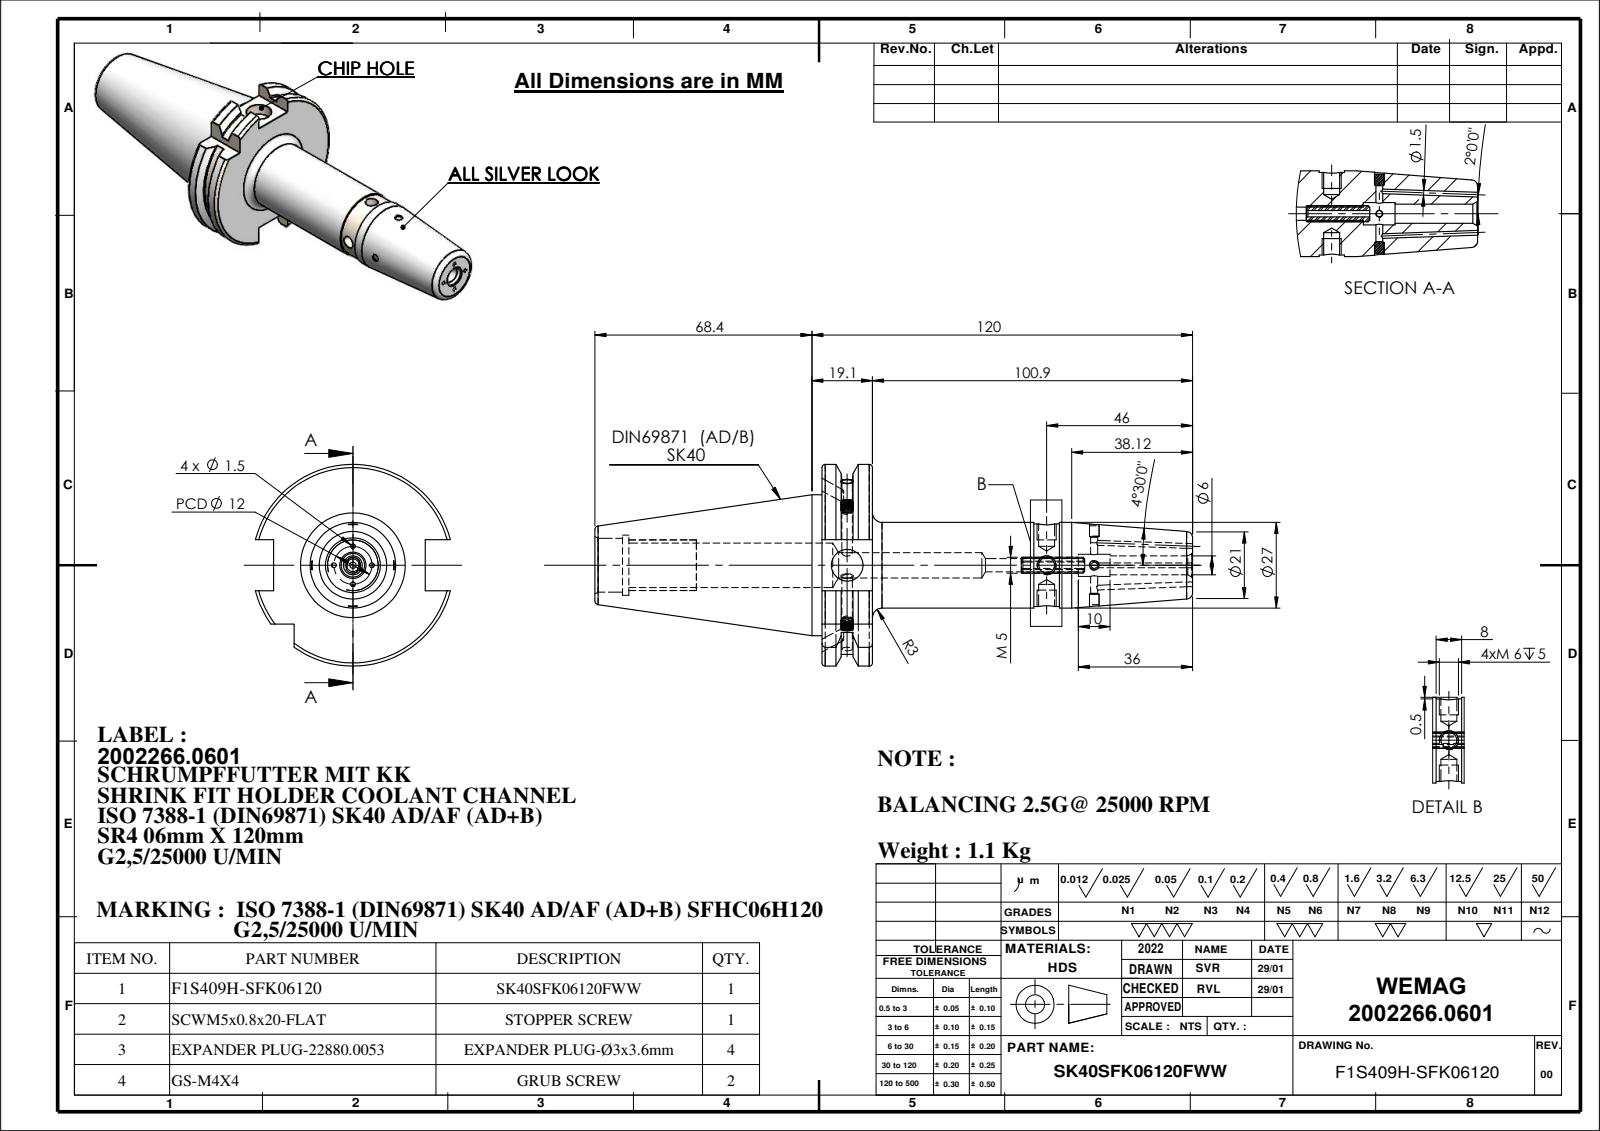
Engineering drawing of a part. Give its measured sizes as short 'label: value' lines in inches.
name: SK40SFK06120FWW; 91406-SR406120; EXPANDER PLUG Ø3x3.6; GS-M4X4_DIN 913 - M4 x 4-N (+1 more)
written by: SolidWorks 2018 (CONFIG_CONTROL_DESIGN)
unit: in
bodies: 8 solids, 295 faces (62 planar, 105 cylindrical, 128 other)
size: 7.417 × 2.502 × 2.42
volume: 9.072 in³; area: 51.59 in²
holes: 4× ⌀0.059, 2× ⌀0.087, 2× ⌀0.118, 2× ⌀0.197, 1× ⌀0.079, 1× ⌀0.13, 1× ⌀0.165, 1× ⌀0.236, 1× ⌀0.275, 1× ⌀0.315, 1× ⌀0.394, 1× ⌀0.551
bosses: 2× ⌀0.157, 1× ⌀1.75, 1× ⌀1.063, 1× ⌀1.024
rounds: 1× R0.098, 1× R1.107, 1× R1.251
face distances: 0.626, 0.634, 1.882, 4.598, 3.972, 0.138, 2.819, 3.445, 7.417, 0.421
hole spacings: 0.591, 2.474, 3.065
